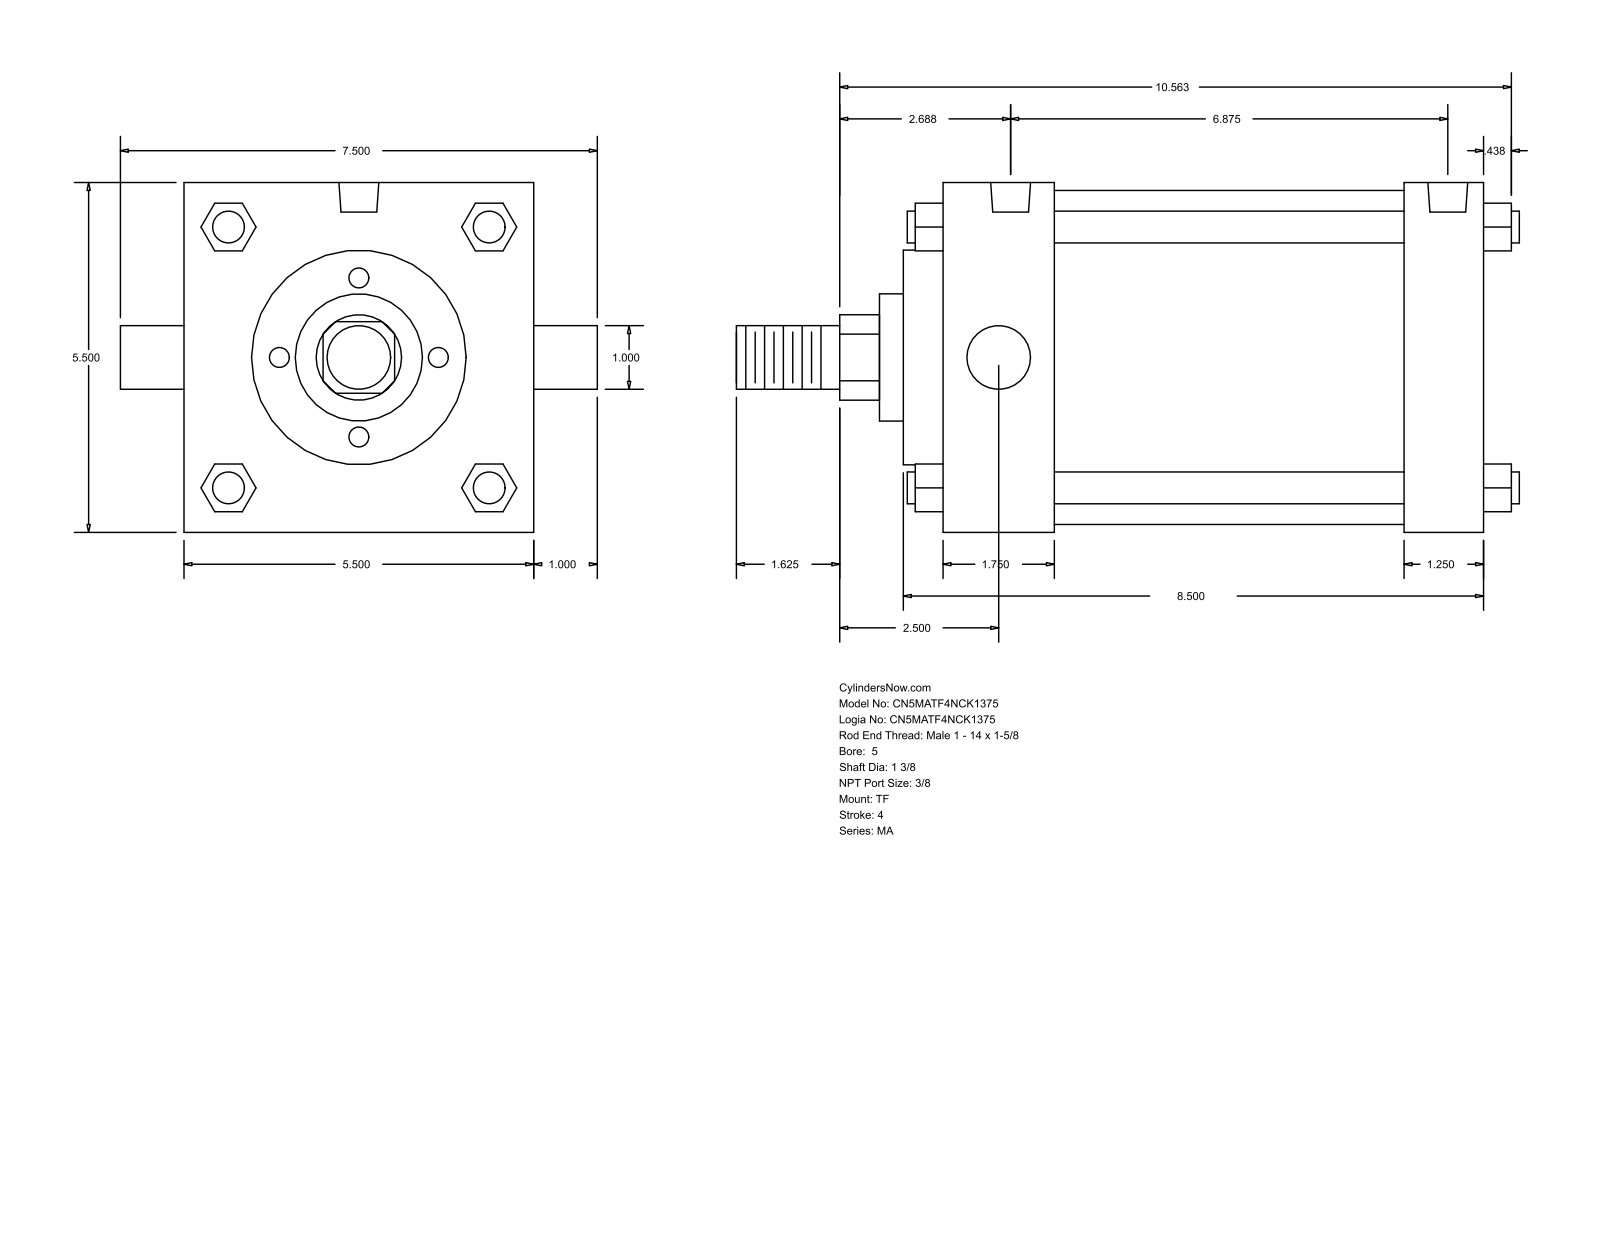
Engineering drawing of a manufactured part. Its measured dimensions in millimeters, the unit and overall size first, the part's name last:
Units: millimetres
Overall size (bounding box): 312.74 × 190.5 × 139.7
Round holes (diameter × count): ⌀11.11 ×3, ⌀15.93 ×2
Round bosses / shafts (diameter × count): ⌀12.7 ×4, ⌀25.4 ×2, ⌀133.35 ×1, ⌀85.72 ×1, ⌀50.8 ×1, ⌀34.92 ×1
Partial cylindrical surfaces — rounded edges, fillets, slot ends (radius × count): R17.06 ×1
Main face-to-face distances: 139.7, 215.91, 184.16, 31.75, 44.45, 139.71, 171.46, 15.87, 60.32, 200.03
Hole centre spacings: 4.77, 169.86, 165.09, 174.63
Bodies: 0 solids, 122 faces (93 planar, 29 cylindrical, 0 other)
Part name (STEP PRODUCT): MA_TF__0500_1.375
STEP written by: GSSL Pune (CONFIG_CONTROL_DESIGN)
